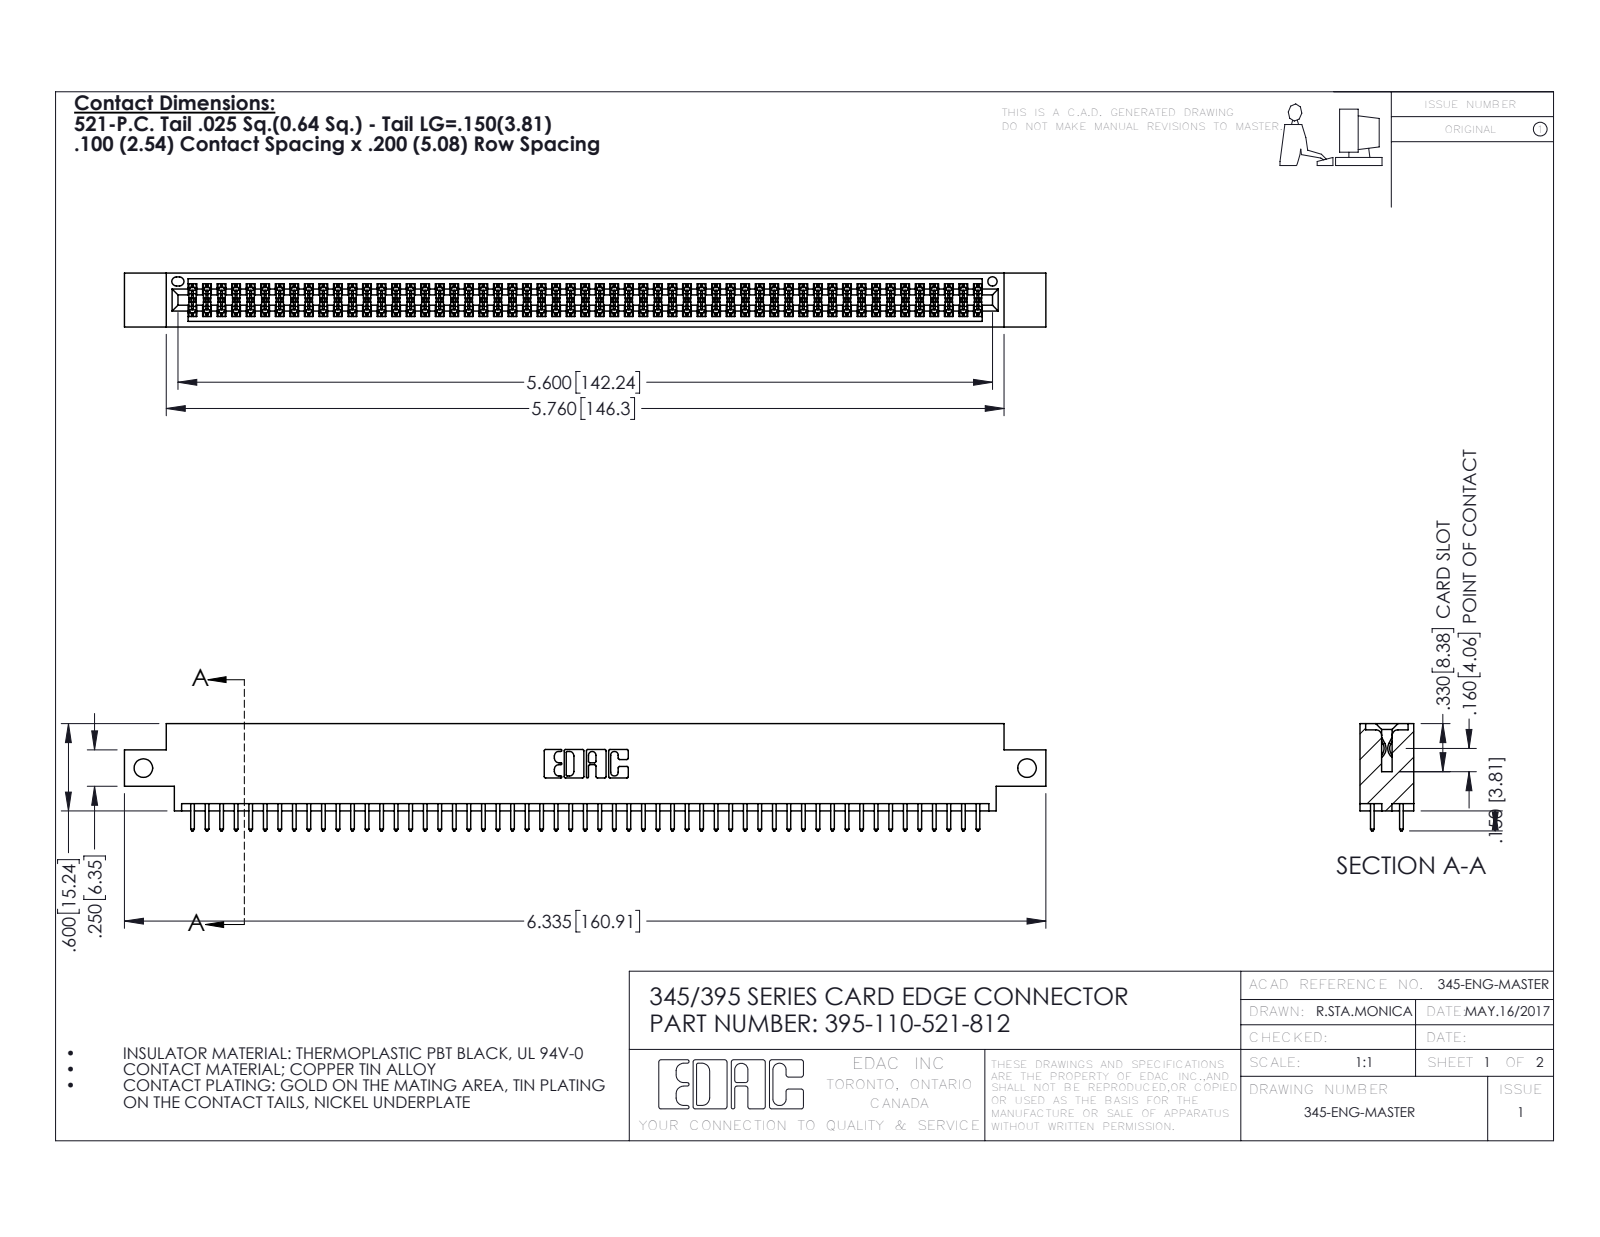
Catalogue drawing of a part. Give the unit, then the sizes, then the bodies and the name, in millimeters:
Units: millimetres
Overall size (bounding box): 160.9 × 18.7 × 9.4
Round holes (diameter × count): ⌀3.3 ×2, ⌀1.6 ×1
Partial cylindrical surfaces — rounded edges, fillets, slot ends (radius × count): R0.2 ×165, R0.3 ×110, R0.3 ×22, R0.2 ×6, R0.8 ×6, R0.7 ×3, R0.4 ×2, R0.5 ×2
Main face-to-face distances: 1.8, 7.6, 9.4, 5.1, 2.5, 6.9, 0.6, 5.7, 4.4, 3.8
Hole centre spacings: 154.3
Volume: 15 500 mm³ · Surface area: 22 890 mm²
Bodies: 111 solids, 5630 faces (3714 planar, 1916 cylindrical, 0 other)
Part name (STEP PRODUCT): 395-110-521-812; 345 Part_0.170 Offset - Side Mount; 345-292-001_345-293-121
STEP written by: SolidWorks 2016 (CONFIG_CONTROL_DESIGN)
